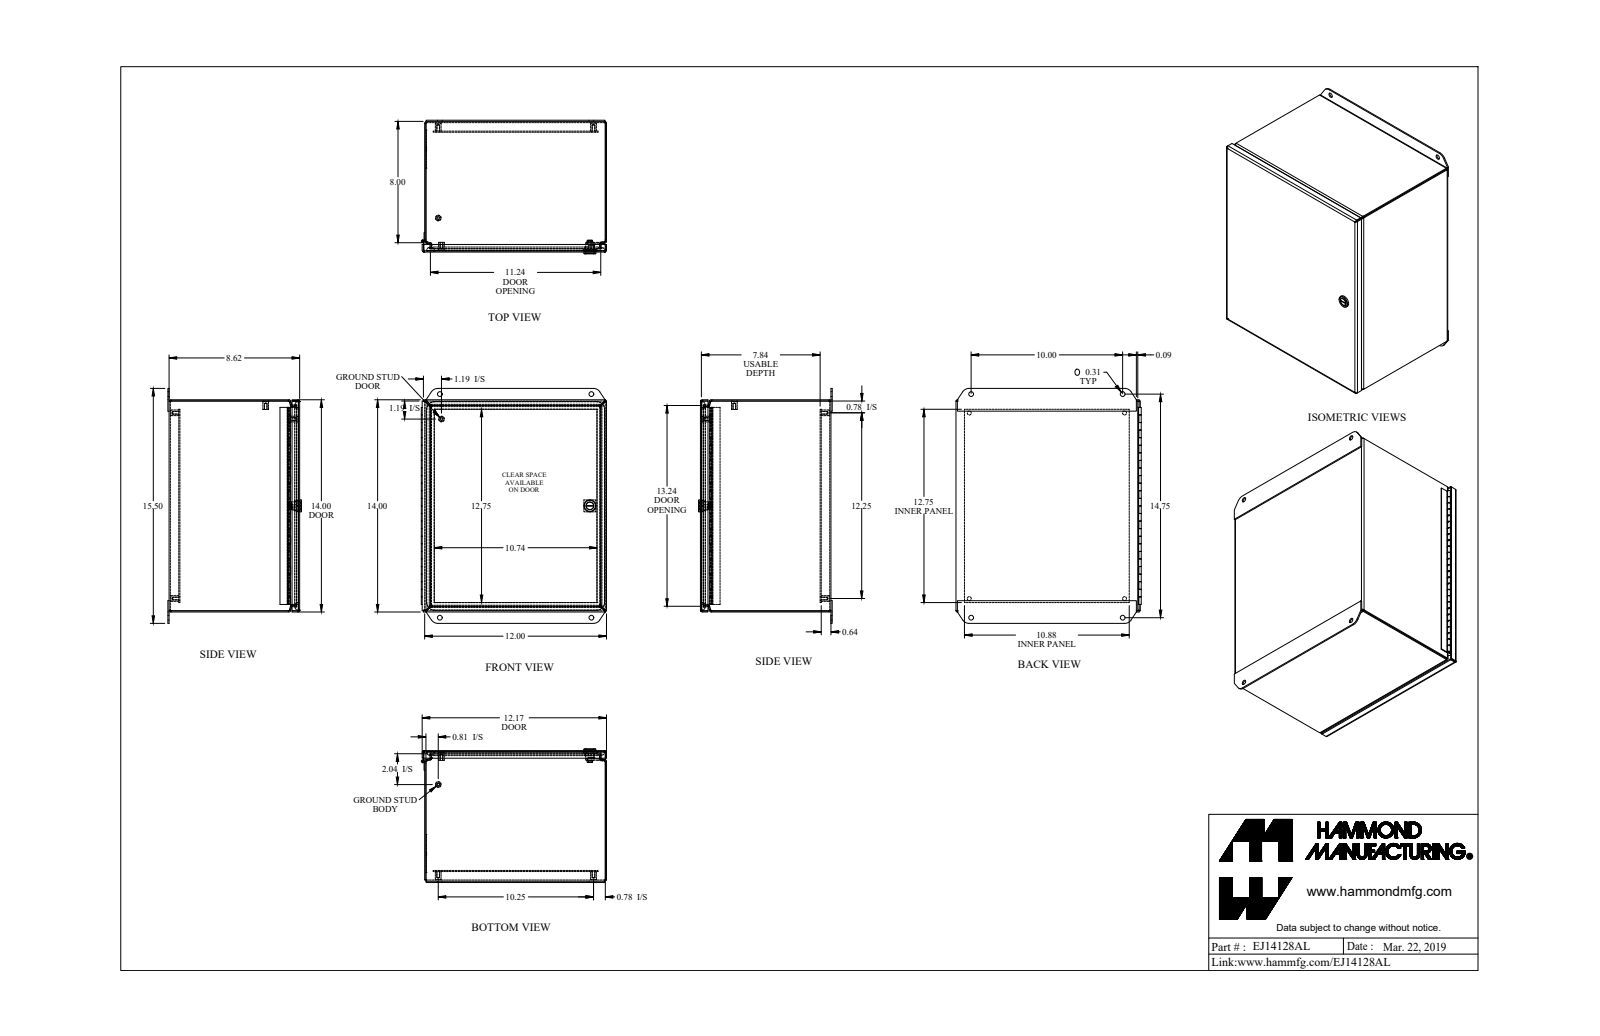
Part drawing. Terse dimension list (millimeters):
name: EJ14128AL_Default
written by: SolidWorks 2019 (CONFIG_CONTROL_DESIGN)
unit: mm
bodies: 14 solids, 694 faces (466 planar, 160 cylindrical, 68 other)
size: 393.7 × 310.5 × 224
volume: 1 365 000 mm³; area: 1 367 000 mm²
holes: 6× ⌀4, 4× ⌀6.7, 4× ⌀8, 1× ⌀13.1
bosses: 6× ⌀9.5, 6× ⌀8.4, 1× ⌀20, 1× ⌀13.6, 1× ⌀12.6, 1× ⌀11, 1× ⌀4.6, 1× ⌀2.5
rounds: 16× R1, 16× R3.1, 12× R7.1, 4× R6.4, 4× R12.7, 4× R12.7, 2× R1.5, 1× R0.8
face distances: 2.1, 216.8, 302.7, 218.9, 353.5, 214.8, 16.3, 14.3, 202.5, 200.5
hole spacings: 31.9, 259.1, 342.9, 405.7, 428.6, 0.6, 155.7, 187.4
